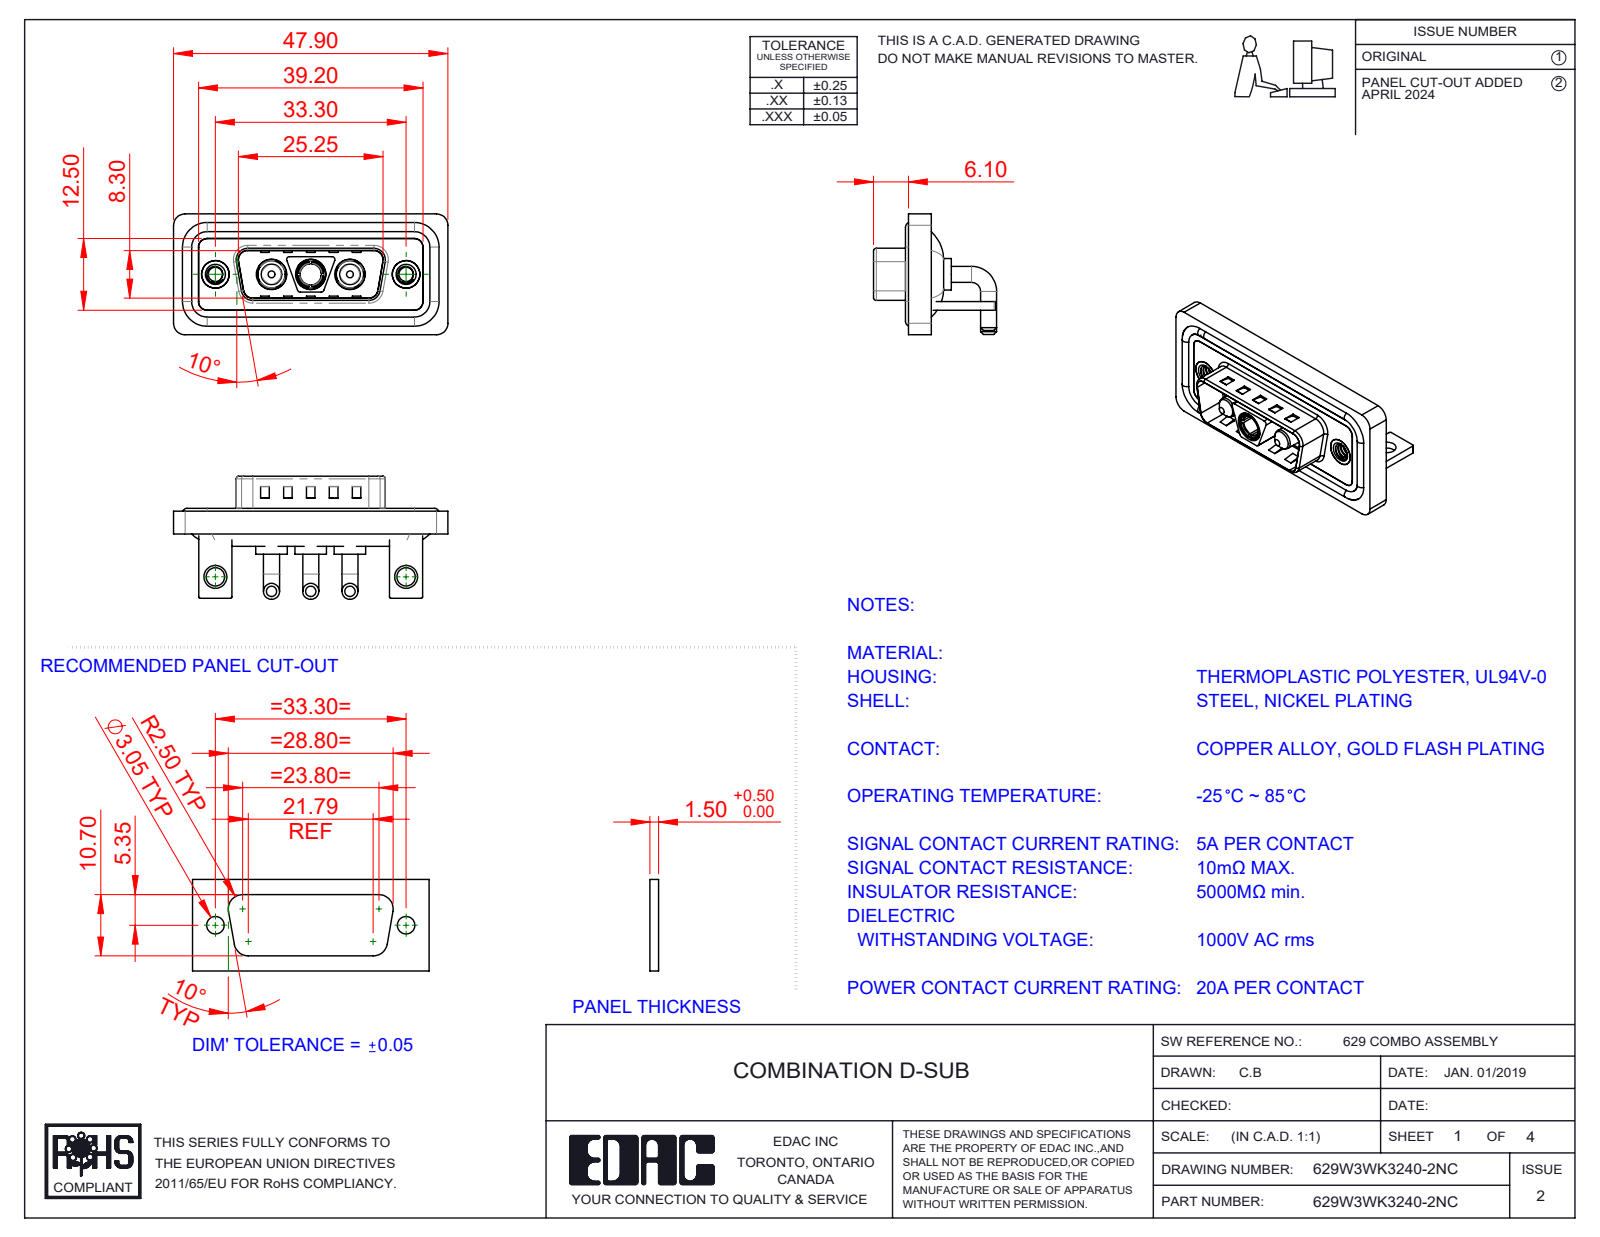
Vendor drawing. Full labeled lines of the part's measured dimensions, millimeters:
Part name (STEP PRODUCT): 629Combo Shell Rear_15 Contacts; 629Combo Waterproof Housing_15 Contacts; 629Combo Shell Front_15 Contacts; 629Combo Stabilizer Bracket (+5 more)
STEP written by: SolidWorks 2023 (CONFIG_CONTROL_DESIGN)
Units: millimetres
Bodies: 15 solids, 659 faces (251 planar, 274 cylindrical, 134 other)
Overall size (bounding box): 47.9 × 21.5 × 21.1
Volume: 6 157 mm³ · Surface area: 10 004 mm²
Round holes (diameter × count): ⌀4.85 ×3, ⌀5.3 ×3, ⌀2.5 ×2, ⌀3.2 ×2, ⌀4 ×2, ⌀4.8 ×2, ⌀5 ×2, ⌀3.7 ×1
Round bosses / shafts (diameter × count): ⌀2.8 ×6, ⌀1.6 ×4, ⌀5.5 ×3, ⌀5.2 ×3, ⌀4.75 ×3, ⌀3.75 ×3, ⌀4.9 ×2, ⌀3.6 ×2
Partial cylindrical surfaces — rounded edges, fillets, slot ends (radius × count): R2 ×21, R1.5 ×18, R0.25 ×16, R0.5 ×13, R1.6 ×8, R0.6 ×4, R0.65 ×4, R0.9 ×4
Main face-to-face distances: 0.4, 1.5, 0.8, 2.9, 1.1, 2.1, 3.7, 1.6, 1.2, 4.5
Hole centre spacings: 6.85, 9.8, 16.65, 23.5, 33.3, 13.7
